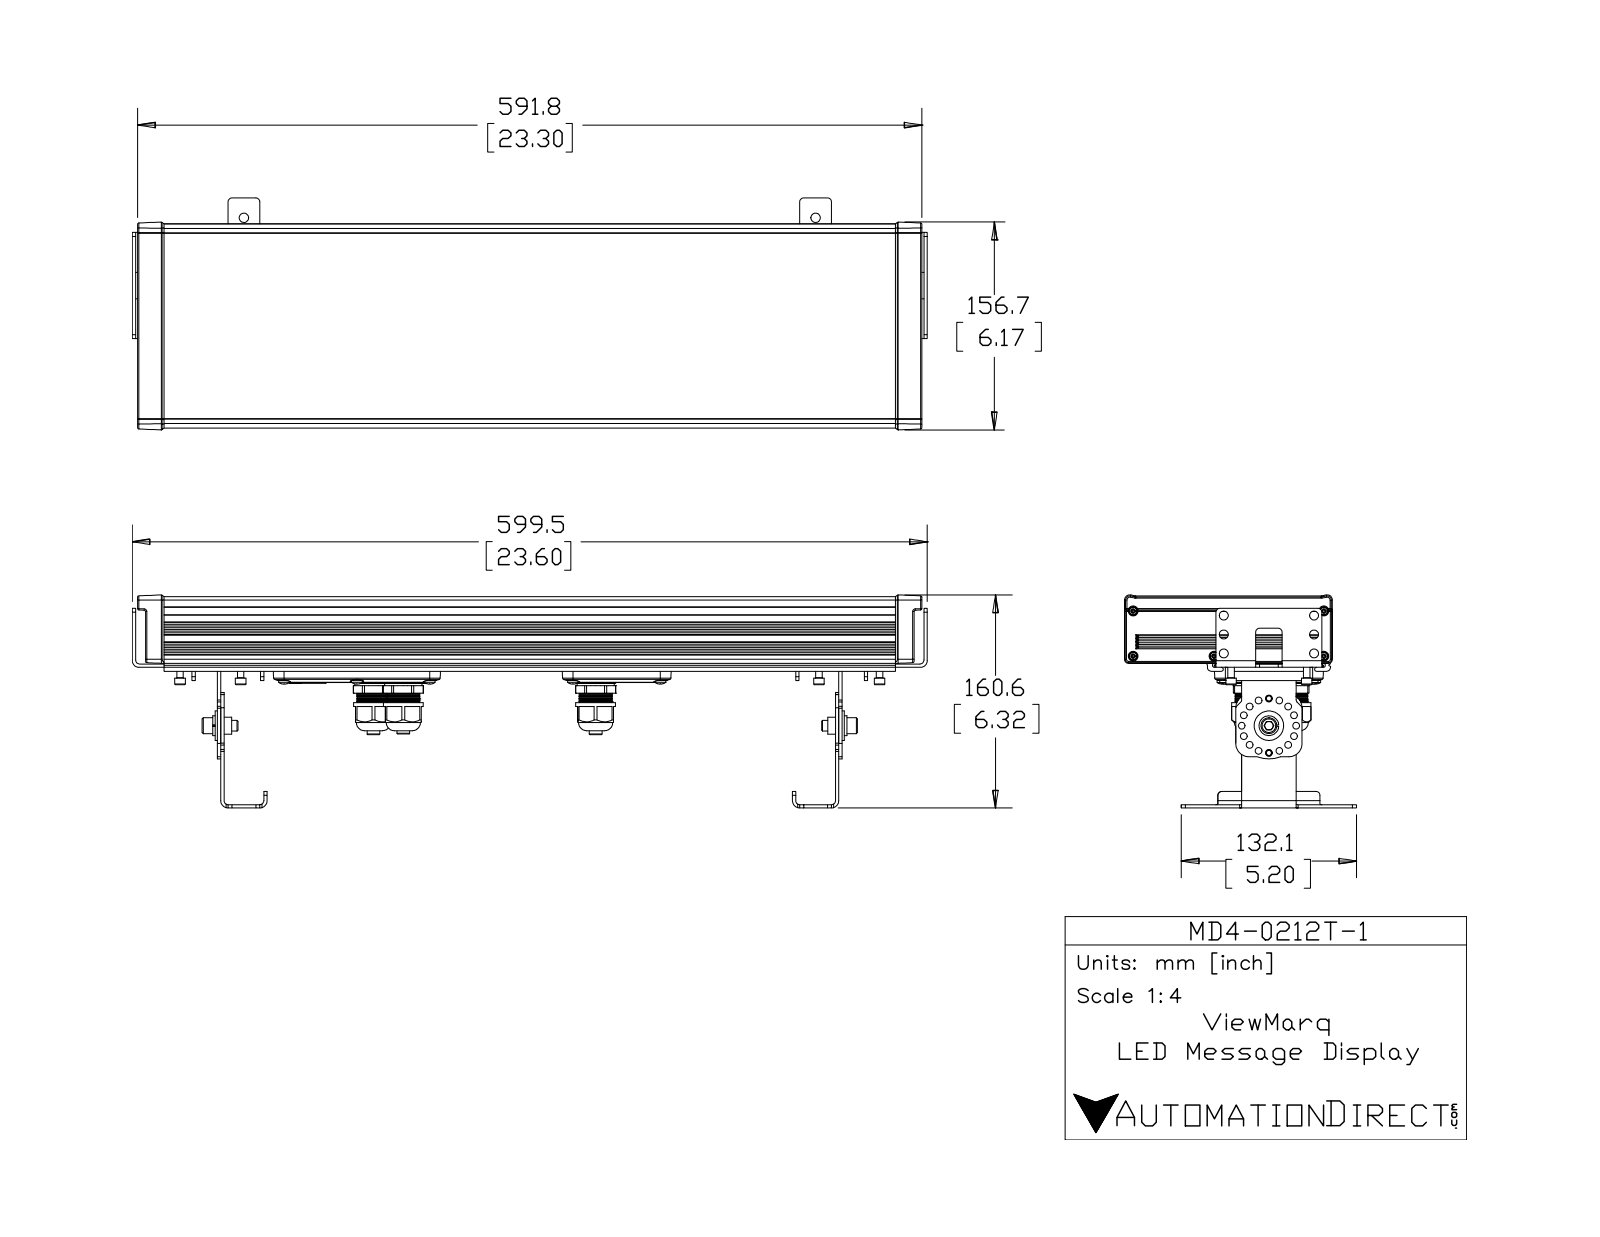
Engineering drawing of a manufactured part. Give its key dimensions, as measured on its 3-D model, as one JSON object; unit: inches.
{"part_name": "MD4-0212T-1", "step_written_by": "SolidWorks 2021 (AUTOMOTIVE_DESIGN)", "units": "inches", "bodies": {"solids": 84, "faces": 6950, "planar": 2118, "cylindrical": 2289, "other": 2543}, "overall_size": [23.602, 6.885, 6.324], "volume_in3": 67.26, "surface_area_in2": 1362, "round_holes": [[0.201, 26], [0.266, 12], [0.281, 12], [0.136, 10], [0.138, 10], [0.165, 10], [0.186, 10], [0.19, 6], [0.118, 5], [0.142, 5], [0.159, 4], [0.533, 3]], "round_bosses_or_shafts": [[0.323, 10], [0.315, 10], [0.159, 10], [0.118, 10], [0.313, 9], [0.091, 8], [0.22, 5], [0.19, 4]], "partial_cylinders_radius": [[0.02, 382], [0.02, 302], [0.01, 140], [0.118, 69], [0.01, 57], [0.039, 54], [0.031, 40], [0.026, 36]], "face_to_face_distances": [0.079, 0.118, 1.735, 1.814, 0.118, 0.098, 1.617, 1.696, 0.119, 0.236], "hole_center_spacings": [0.807, 1.342, 1.491, 0.315, 0.897, 1.141, 1.583, 2.591]}
